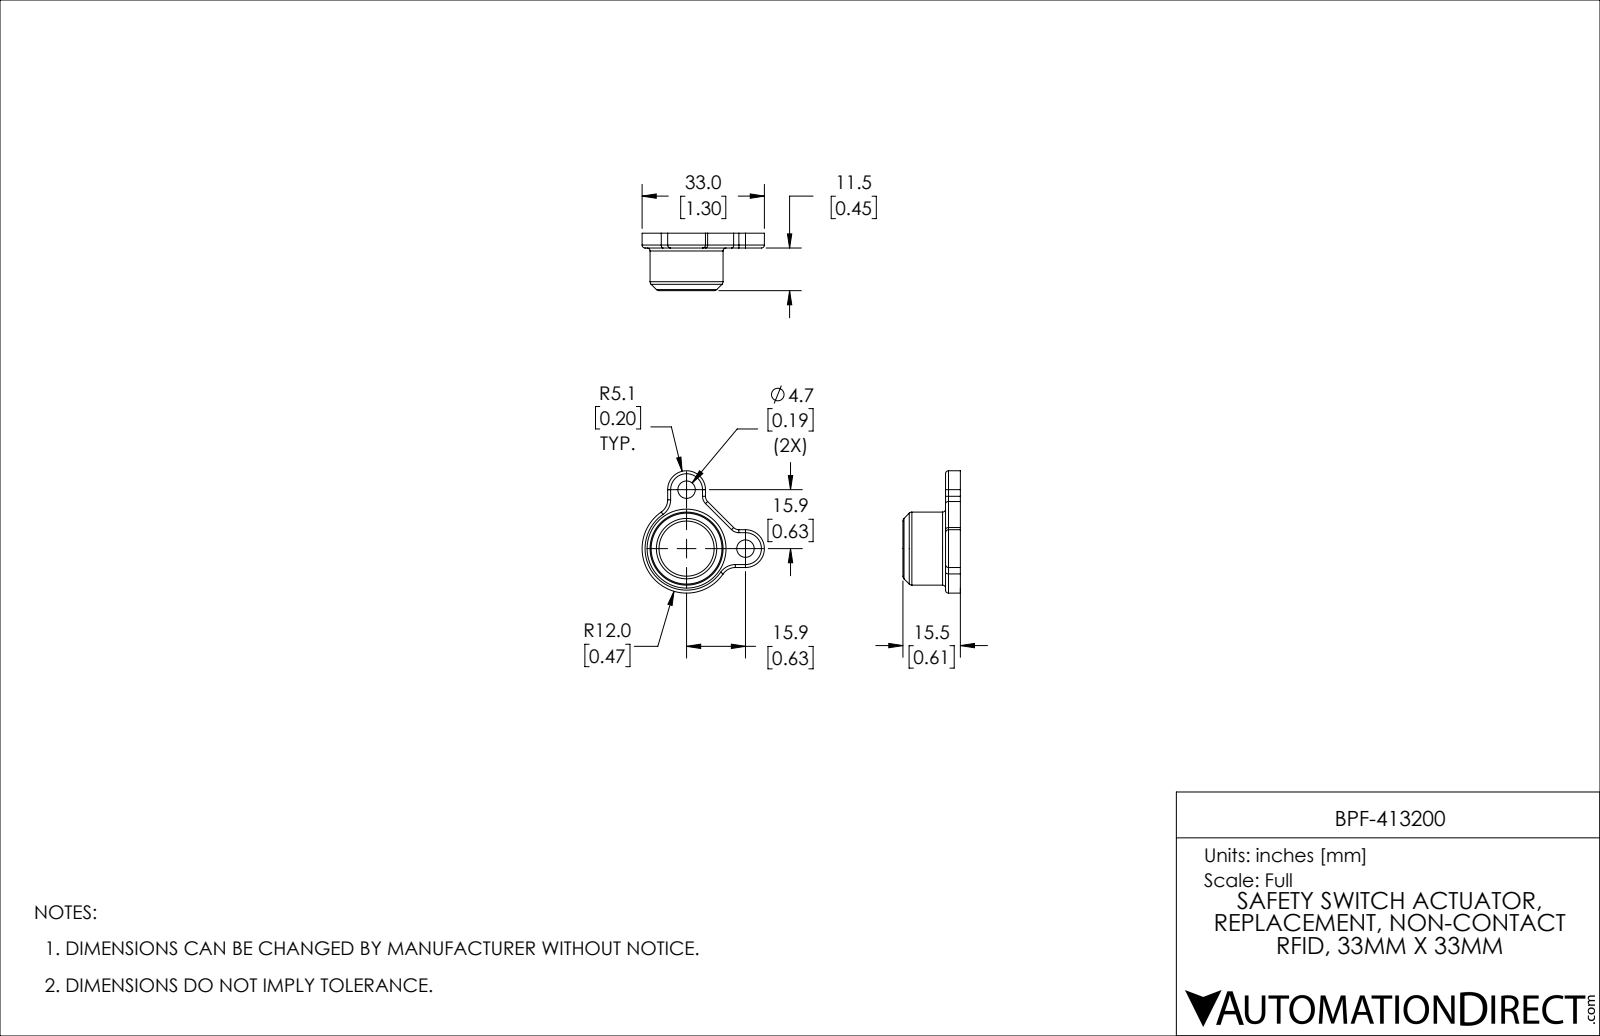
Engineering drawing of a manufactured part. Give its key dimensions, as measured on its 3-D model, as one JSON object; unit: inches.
{"part_name": "BPF-413200", "step_written_by": "SolidWorks 2019 (AUTOMOTIVE_DESIGN)", "units": "inches", "bodies": {"solids": 2, "faces": 68, "planar": 19, "cylindrical": 25, "other": 24}, "overall_size": [1.299, 1.299, 0.61], "volume_in3": 0.22, "surface_area_in2": 6.378, "round_holes": [[0.098, 4], [0.185, 2], [0.079, 1], [0.528, 1], [0.63, 1], [0.709, 1]], "round_bosses_or_shafts": [[0.776, 1], [0.622, 1]], "partial_cylinders_radius": [[0.031, 5], [0.079, 2], [0.157, 2], [0.201, 2], [0.472, 1]], "face_to_face_distances": [0.059, 0.539, 0.61, 0.598, 0.157, 0.146, 0.453, 0.071, 0.087, 0.551], "hole_center_spacings": [0.191, 0.481, 0.217, 0.626, 0.68, 0.698, 0.871, 0.509]}
